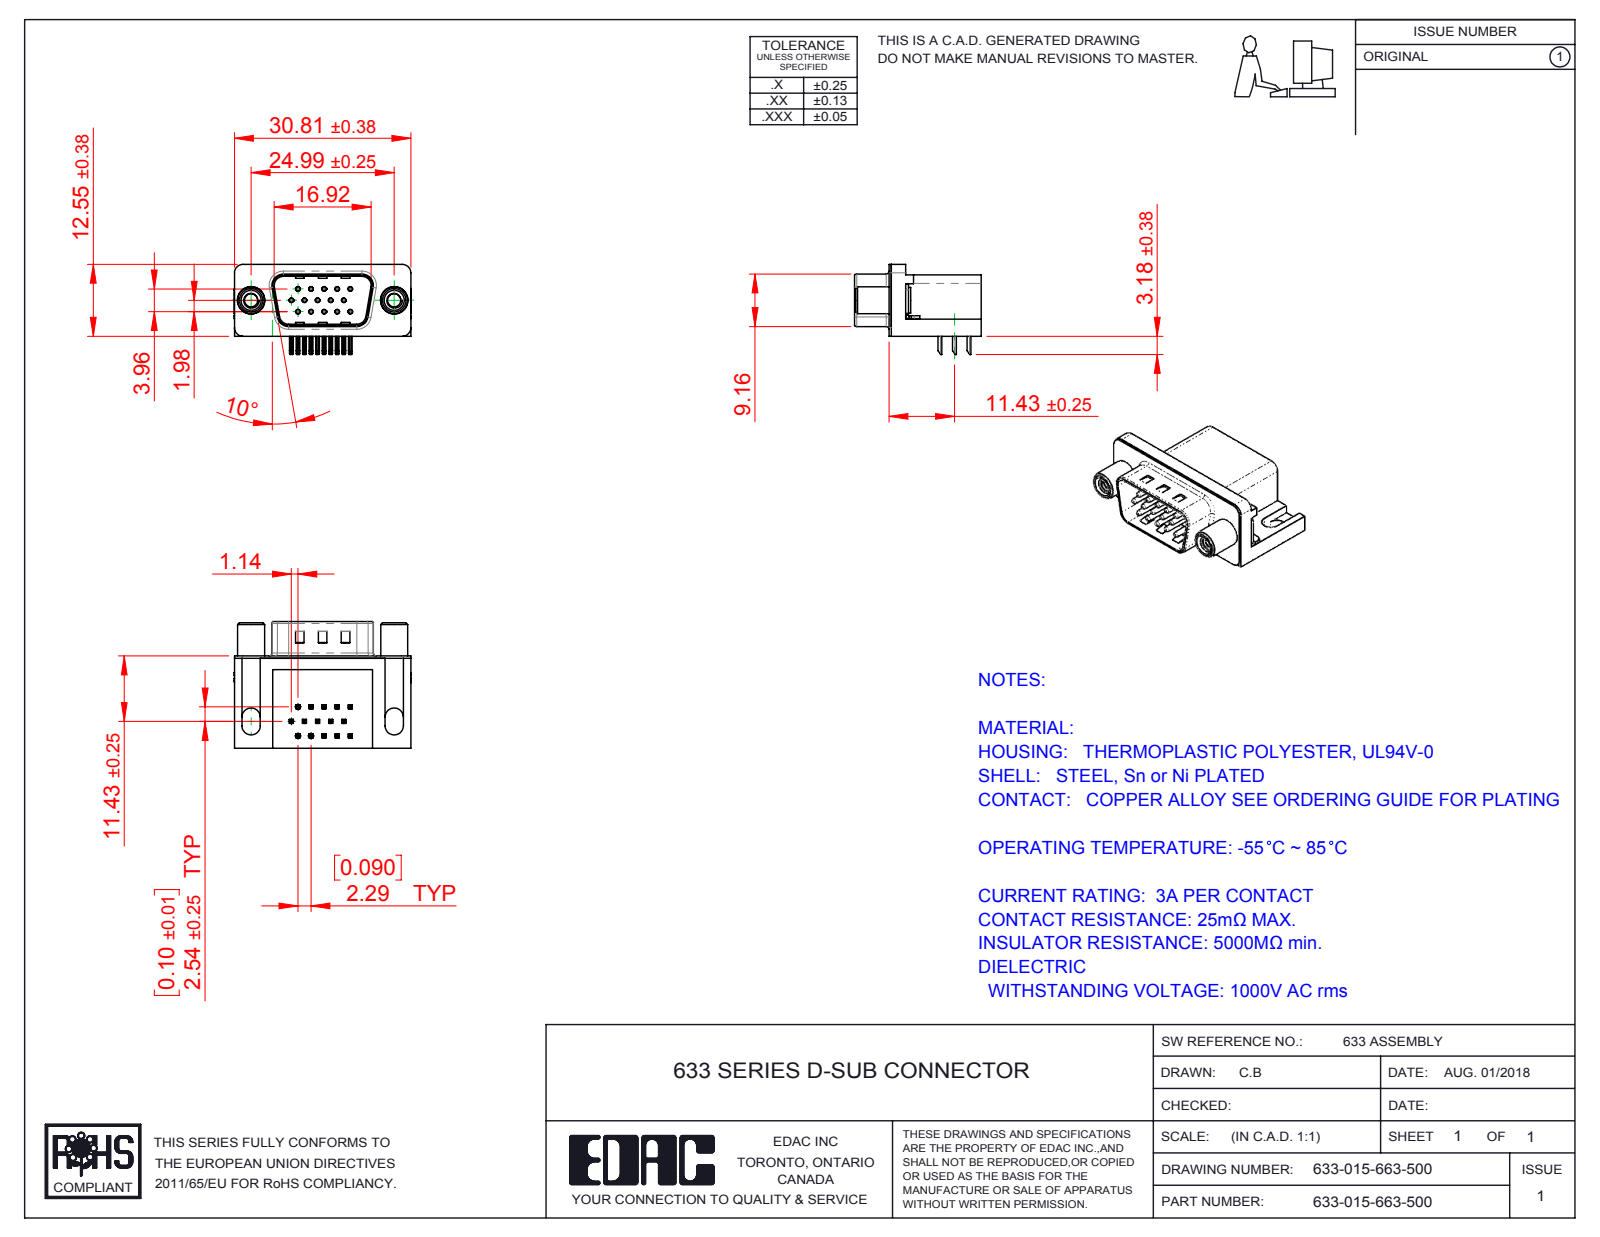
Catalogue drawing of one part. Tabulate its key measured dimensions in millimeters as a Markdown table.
| quantity | value |
| --- | --- |
| part name | 633 Housing_15 Contact; 633 Contact Bottom; 633 Contact Middle; 633 Shell_15 Contact (+4 more) |
| STEP written by | SolidWorks 2016 (CONFIG_CONTROL_DESIGN) |
| units | millimeters |
| bodies | 21 solids, 1433 faces (853 planar, 447 cylindrical, 133 other) |
| overall size | 30.89 × 22.1 × 15.73 |
| volume | 4 116 mm³ |
| surface area | 5 401 mm² |
| round holes (diameter × count) | 0.35 × 15, 0.8 × 15, 2.3 × 2, 3.1 × 2, 4 × 2, 4.8 × 2, 5 × 2 |
| round bosses / shafts (diameter × count) | 0.75 × 15, 4.9 × 2, 4.7 × 2, 4.5 × 2, 3.85 × 2 |
| partial cylindrical surfaces (radius × count) | 0.25 × 60, 0.12 × 30, 1 × 16, 0.5 × 9, 1.6 × 8, 1.5 × 7, 0.9 × 4, 2 × 4 |
| main face-to-face distances | 0.4, 10.35, 15.7, 2.9, 6.7, 2.5, 16.1, 0.35, 10.7, 13.2 |
| hole center spacings | 3.96, 2.28, 4.57, 2.29, 6.05, 6.86, 7.92, 6.04 |
